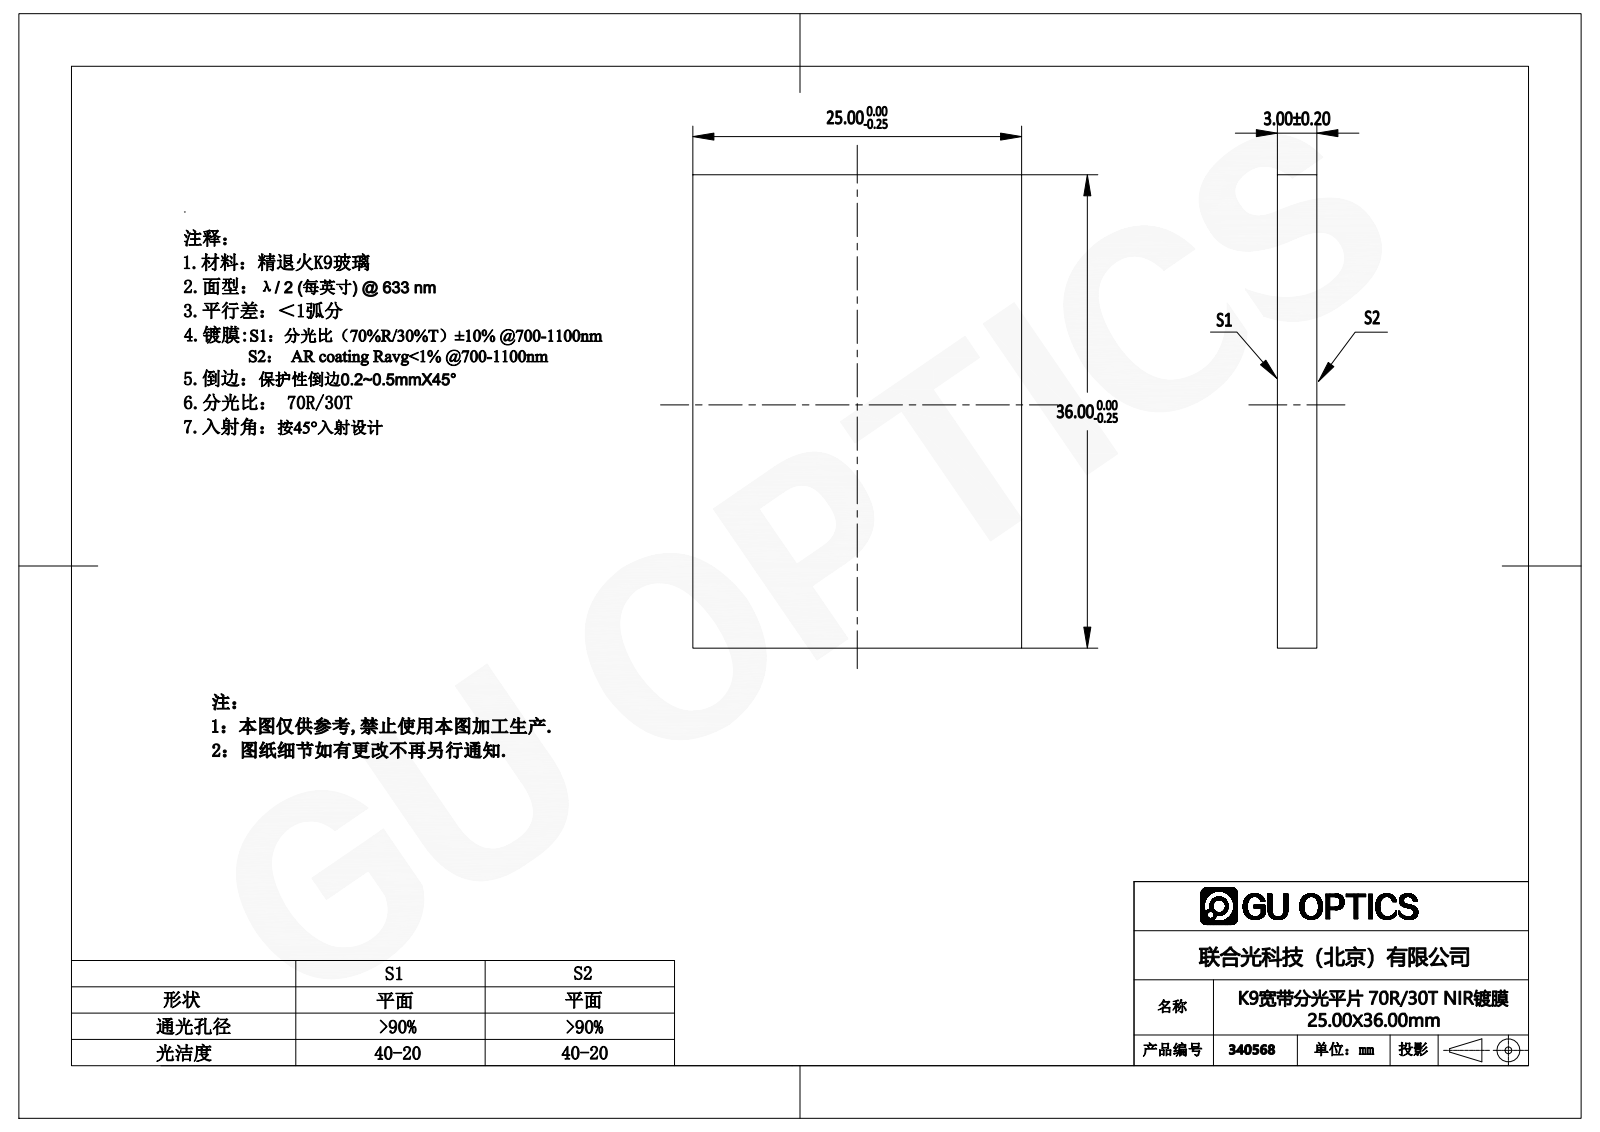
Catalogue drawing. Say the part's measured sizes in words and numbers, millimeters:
The part is named "340525". Its 3-D file was written by "SolidWorks 2016 (CONFIG_CONTROL_DESIGN)". It is 1 solid with 6 faces: 6 planar, 0 cylindrical and 0 other. Overall it measures 36 by 25 by 3 millimeters. Its volume is 2 700 cubic millimeters and its surface area 2 166 square millimeters. The main face-to-face distances are 3, 25, 36.
